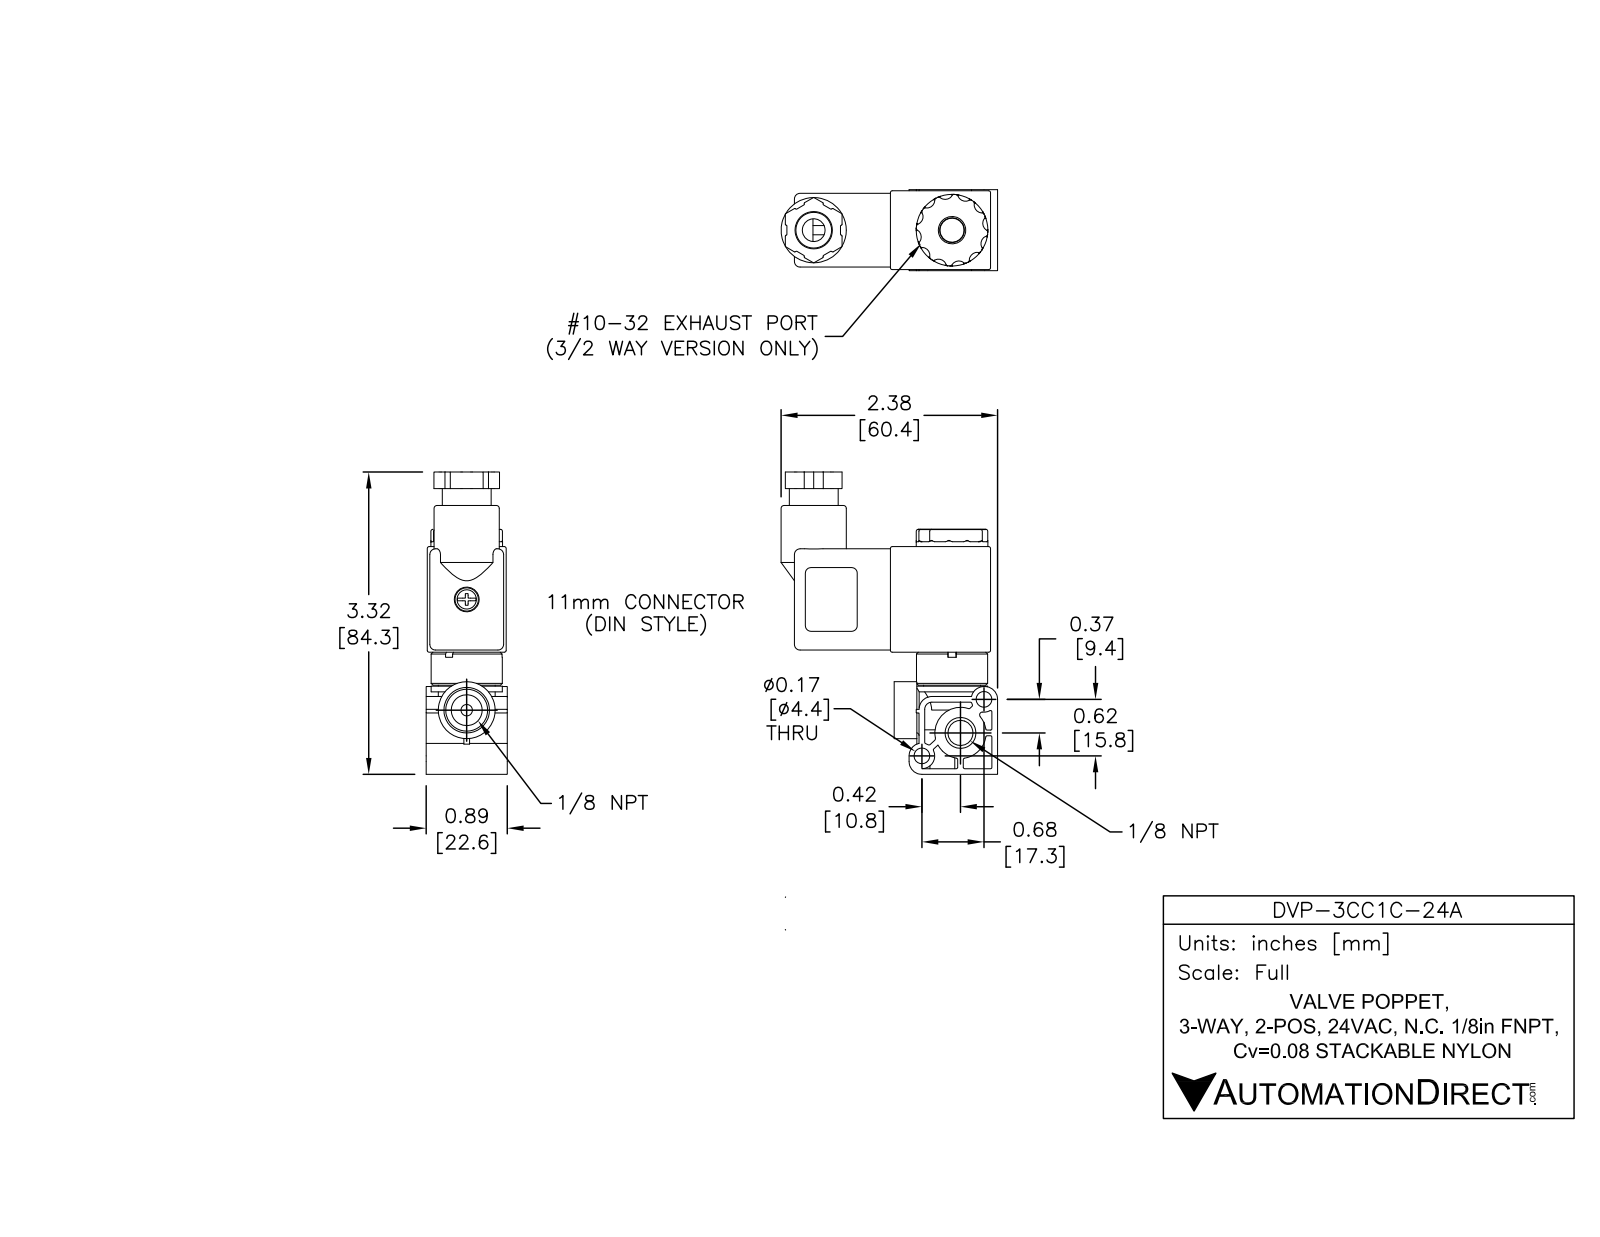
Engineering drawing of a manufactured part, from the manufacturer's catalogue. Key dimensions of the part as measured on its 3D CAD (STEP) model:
Part name (STEP PRODUCT): DVP-3CC1C-24A
STEP written by: SolidWorks 2015 (AUTOMOTIVE_DESIGN)
Units: inches
Bodies: 5 solids, 1465 faces (664 planar, 318 cylindrical, 483 other)
Overall size (bounding box): 3.309 × 2.377 × 0.89
Volume: 2.128 in³ · Surface area: 39.24 in²
Round holes (diameter × count): ⌀0.1 ×2, ⌀0.125 ×2, ⌀0.15 ×2, ⌀0.172 ×2, ⌀0.339 ×2, ⌀0.057 ×1, ⌀0.09 ×1, ⌀0.102 ×1, ⌀0.166 ×1, ⌀0.196 ×1, ⌀0.25 ×1, ⌀0.268 ×1
Round bosses / shafts (diameter × count): ⌀0.625 ×2, ⌀0.787 ×1, ⌀0.781 ×1, ⌀0.716 ×1, ⌀0.652 ×1, ⌀0.572 ×1, ⌀0.536 ×1, ⌀0.522 ×1
Partial cylindrical surfaces — rounded edges, fillets, slot ends (radius × count): R0.015 ×28, R0.01 ×25, R0.025 ×24, R0.02 ×12, R0.062 ×12, R0.088 ×12, R0.031 ×5, R0.141 ×4
Main face-to-face distances: 0.078, 0.788, 0.05, 0.8, 0.76, 0.028, 0.838, 0.866, 0.71, 0.878
Hole centre spacings: 0.327, 0.42, 0.45, 0.493, 0.522, 0.731, 0.922, 0.944
